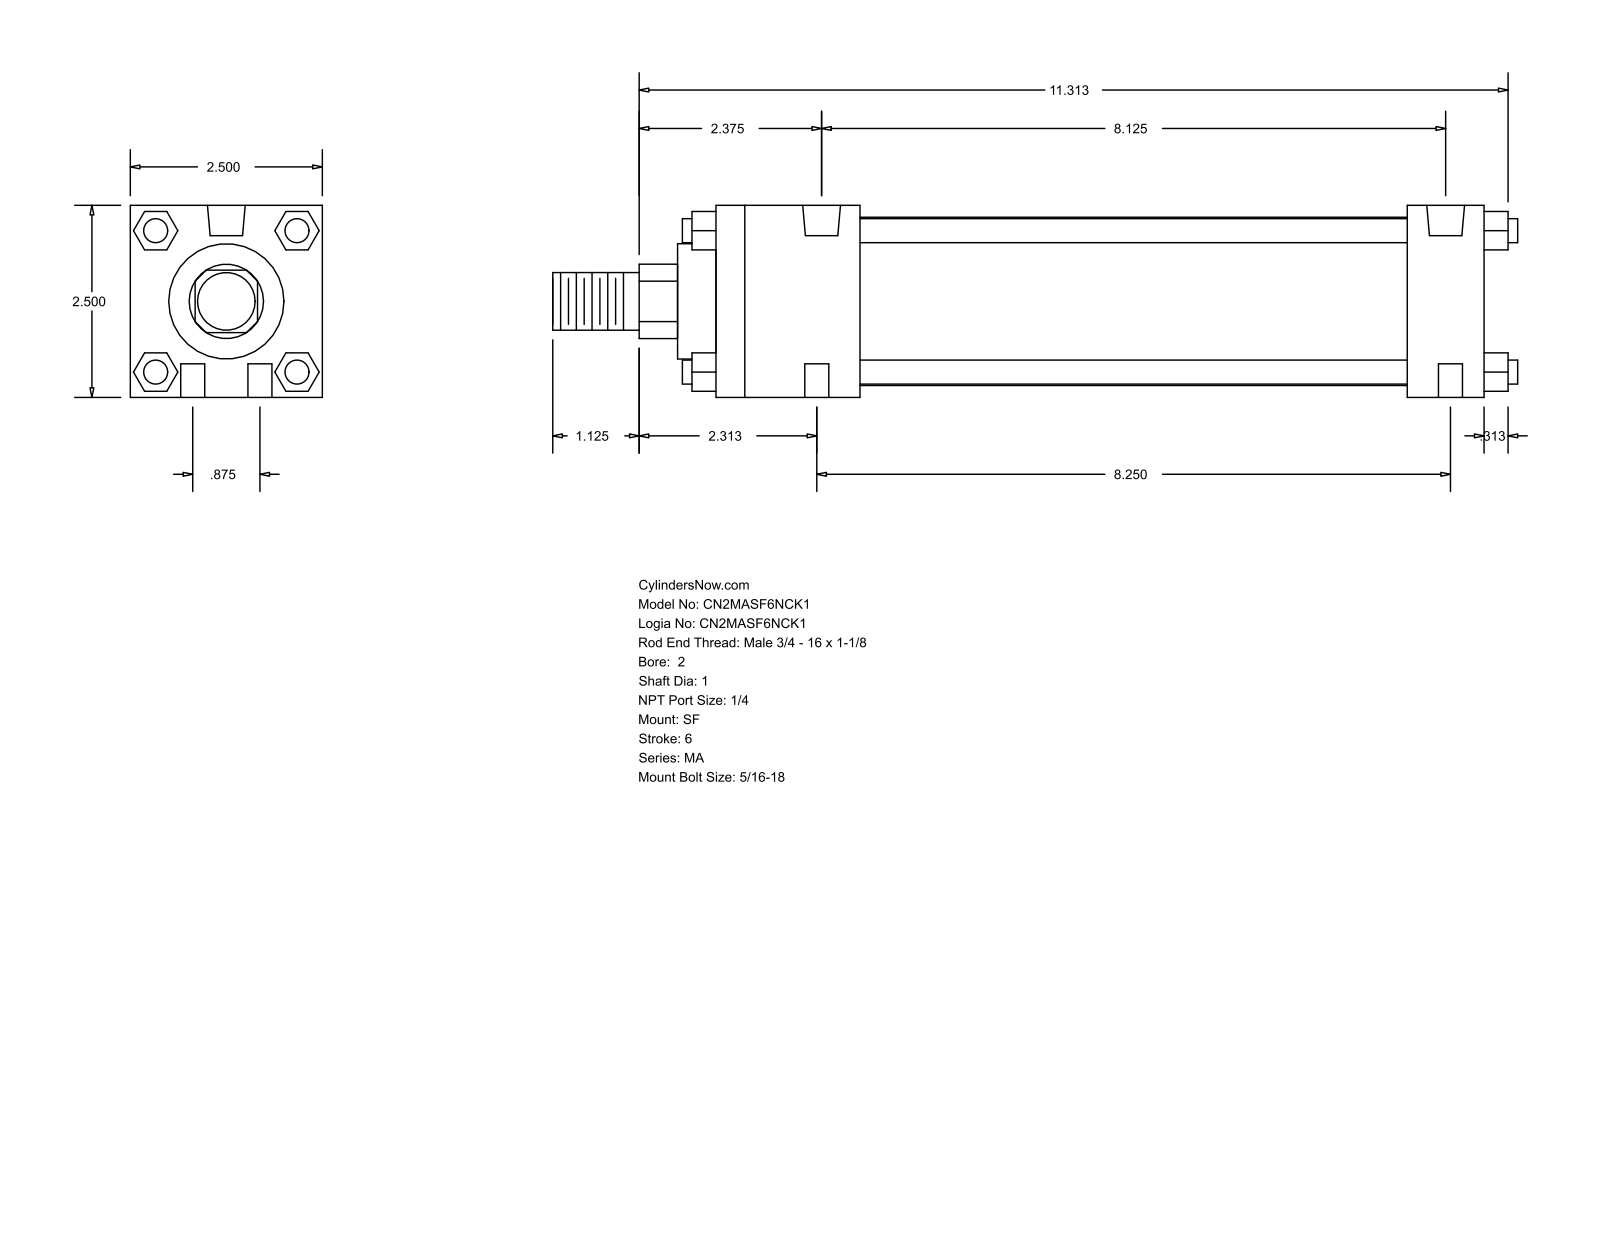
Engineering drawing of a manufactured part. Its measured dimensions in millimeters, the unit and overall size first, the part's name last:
Units: millimetres
Overall size (bounding box): 319.09 × 63.5 × 63.5
Round holes (diameter × count): ⌀7.94 ×6, ⌀12.49 ×2
Round bosses / shafts (diameter × count): ⌀7.94 ×4, ⌀55.63 ×1, ⌀38.1 ×1, ⌀25.4 ×1, ⌀19.05 ×1
Partial cylindrical surfaces — rounded edges, fillets, slot ends (radius × count): R12.29 ×1
Main face-to-face distances: 63.5, 254, 12.7, 25.4, 228.6, 47.63, 180.97, 206.37, 23.37, 40.47
Hole centre spacings: 11.22, 208.26, 22.22, 206.37, 209.55, 210.72
Bodies: 0 solids, 124 faces (94 planar, 30 cylindrical, 0 other)
Part name (STEP PRODUCT): MA_SF__0200_1
STEP written by: GSSL Pune (CONFIG_CONTROL_DESIGN)
